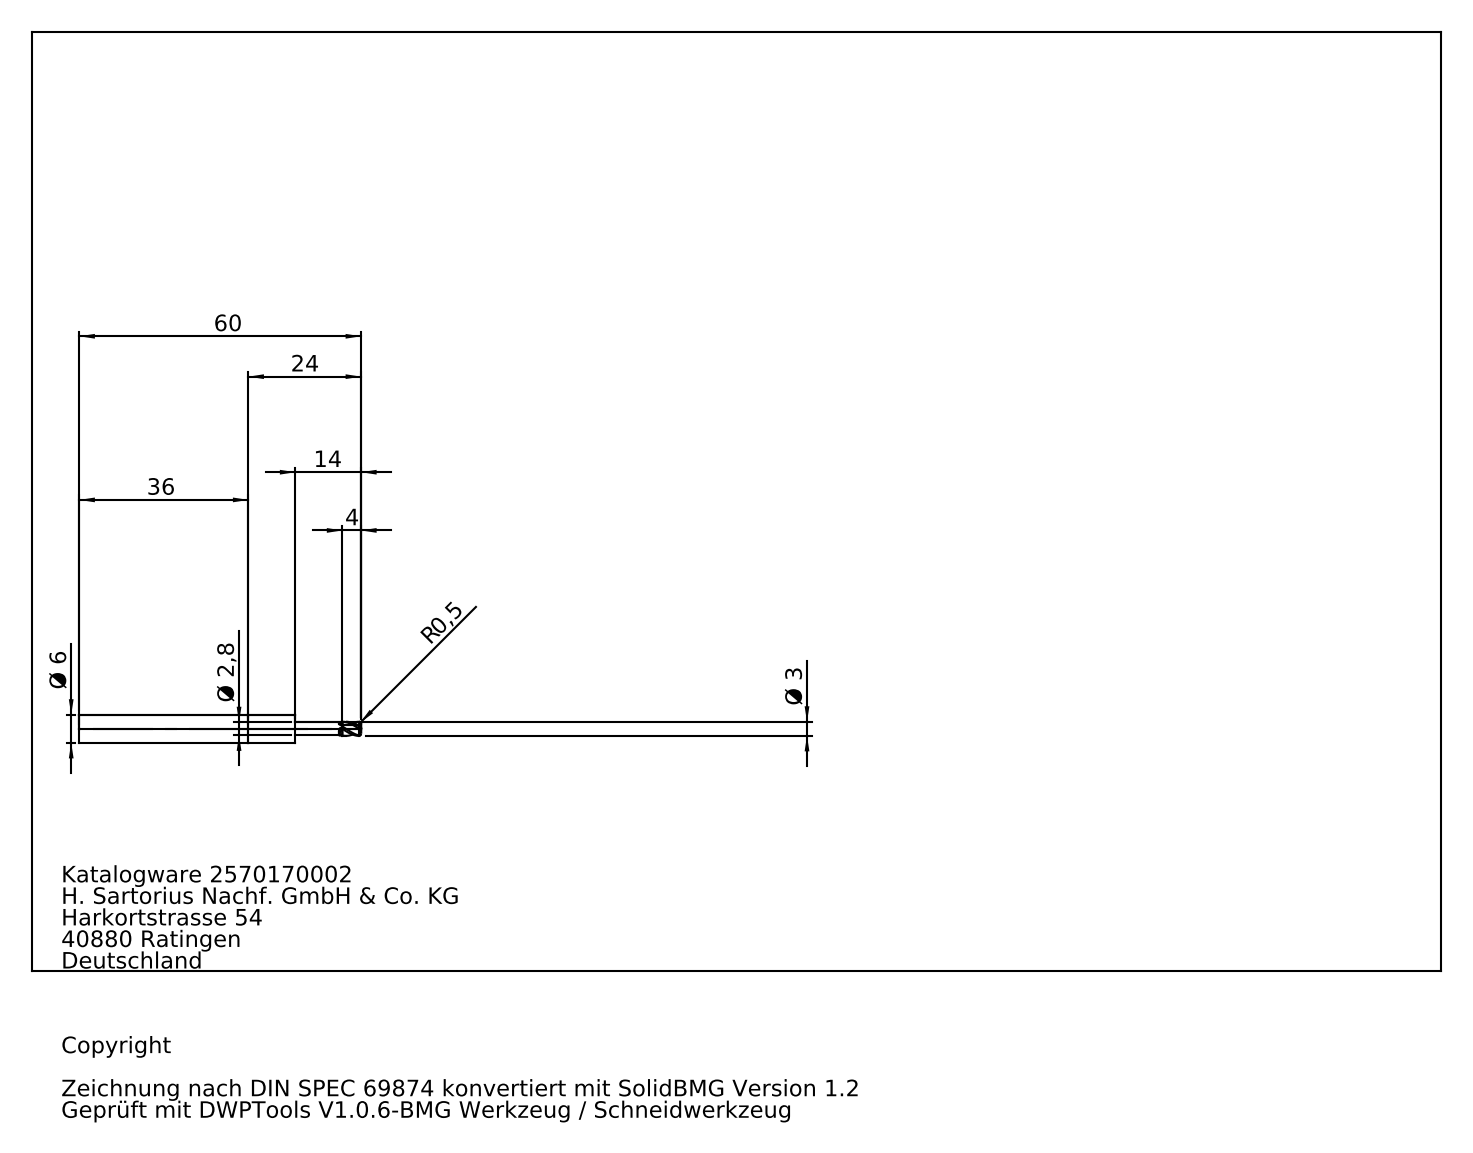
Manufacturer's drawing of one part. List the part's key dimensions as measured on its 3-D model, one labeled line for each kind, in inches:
Part name (STEP PRODUCT): 2570170002
STEP written by: SolidWorks 2010 (AUTOMOTIVE_DESIGN)
Units: inches
Bodies: 2 solids, 59 faces (15 planar, 17 cylindrical, 27 other)
Overall size (bounding box): 2.362 × 0.236 × 0.236
Volume: 0.084 in³ · Surface area: 1.703 in²
Round holes (diameter × count): ⌀0.071 ×1
Round bosses / shafts (diameter × count): ⌀0.236 ×1, ⌀0.118 ×1, ⌀0.11 ×1
Main face-to-face distances: 1.811, 2.343, 0.531, 2.205, 0.394, 0.138, 2.362, 0.551, 0.157, 0.019
